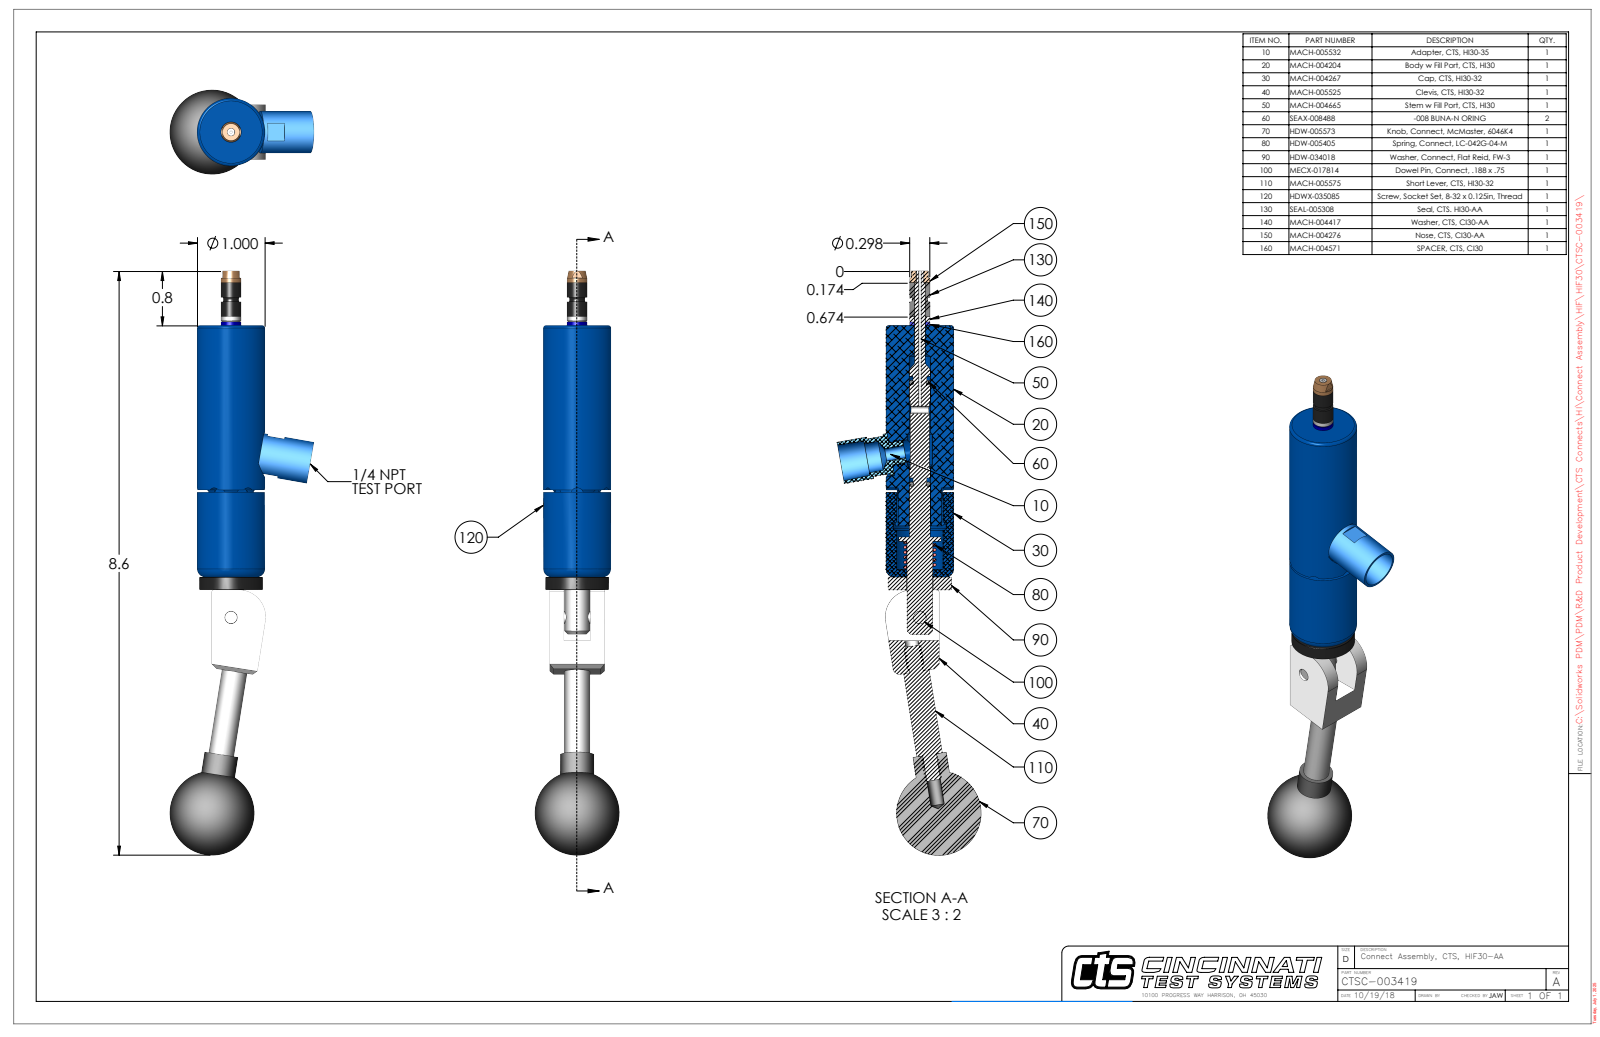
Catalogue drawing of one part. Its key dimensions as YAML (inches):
part_name: "CTSC-003419"
step_written_by: "SolidWorks 2023 (AUTOMOTIVE_DESIGN)"
units: inches
bodies: {solids: 10, faces: 282, planar: 98, cylindrical: 123, other: 61}
overall_size: [8.63, 2.128, 1.25]
volume: 4.92
surface_area: 36.64
round_holes:
  - {diameter: 0.201, count: 2}
  - {diameter: 0.04, count: 1}
  - {diameter: 0.078, count: 1}
  - {diameter: 0.113, count: 1}
  - {diameter: 0.136, count: 1}
  - {diameter: 0.15, count: 1}
  - {diameter: 0.155, count: 1}
  - {diameter: 0.161, count: 1}
  - {diameter: 0.164, count: 1}
  - {diameter: 0.187, count: 1}
  - {diameter: 0.189, count: 1}
  - {diameter: 0.385, count: 1}
round_bosses_or_shafts:
  - {diameter: 1, count: 1}
  - {diameter: 0.936, count: 1}
  - {diameter: 0.62, count: 1}
  - {diameter: 0.5, count: 1}
  - {diameter: 0.38, count: 1}
  - {diameter: 0.375, count: 1}
  - {diameter: 0.3, count: 1}
  - {diameter: 0.297, count: 1}
partial_cylinders:
  - {radius: 0.093, count: 6}
  - {radius: 0.015, count: 1}
  - {radius: 0.054, count: 1}
  - {radius: 0.325, count: 1}
  - {radius: 0.4, count: 1}
  - {radius: 0.457, count: 1}
face_to_face_distances: [0.21, 0.602, 0.812, 0.187, 3.717, 3.904, 0.391, 2.463, 1.253, 1.441]
hole_center_spacings: [0.599, 1.658, 2.252]
